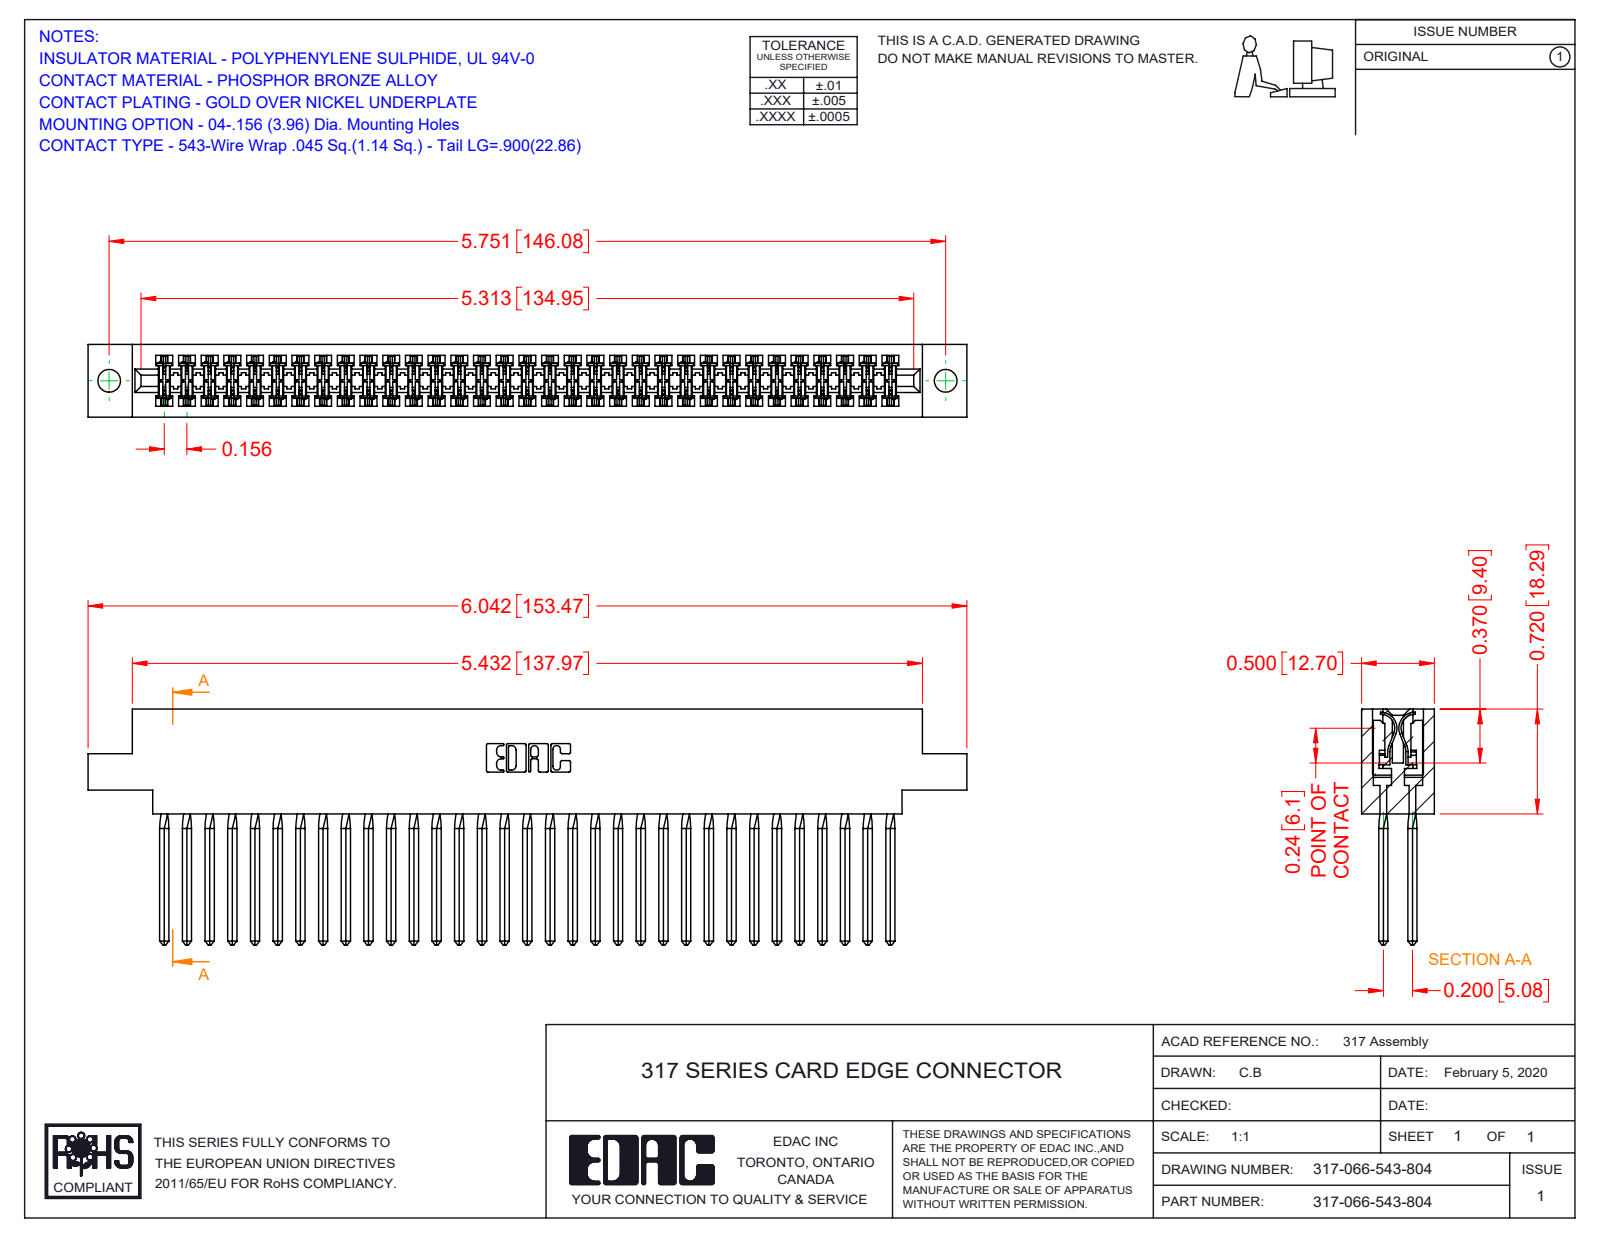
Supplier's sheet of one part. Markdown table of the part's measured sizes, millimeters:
| quantity | value |
| --- | --- |
| part name | 317-066-543-804; 317-290-001_543; 317 Part_.156 Dia - TH |
| STEP written by | SolidWorks 2016 (CONFIG_CONTROL_DESIGN) |
| units | millimeters |
| bodies | 67 solids, 5976 faces (4876 planar, 836 cylindrical, 264 other) |
| overall size | 153.5 × 41.1 × 12.7 |
| volume | 25 690 mm³ |
| surface area | 38 450 mm² |
| round holes (diameter × count) | 4 × 2 |
| partial cylindrical surfaces (radius × count) | 0.4 × 132, 0.3 × 22, 0.2 × 6, 0.8 × 6, 0.7 × 3, 2.4 × 2, 2.5 × 2, 2.8 × 2 |
| main face-to-face distances | 12.7, 1.9, 10.8, 8.9, 2.8, 5, 2.4, 5.1, 2.9, 3.3 |
| hole center spacings | 146.1 |
